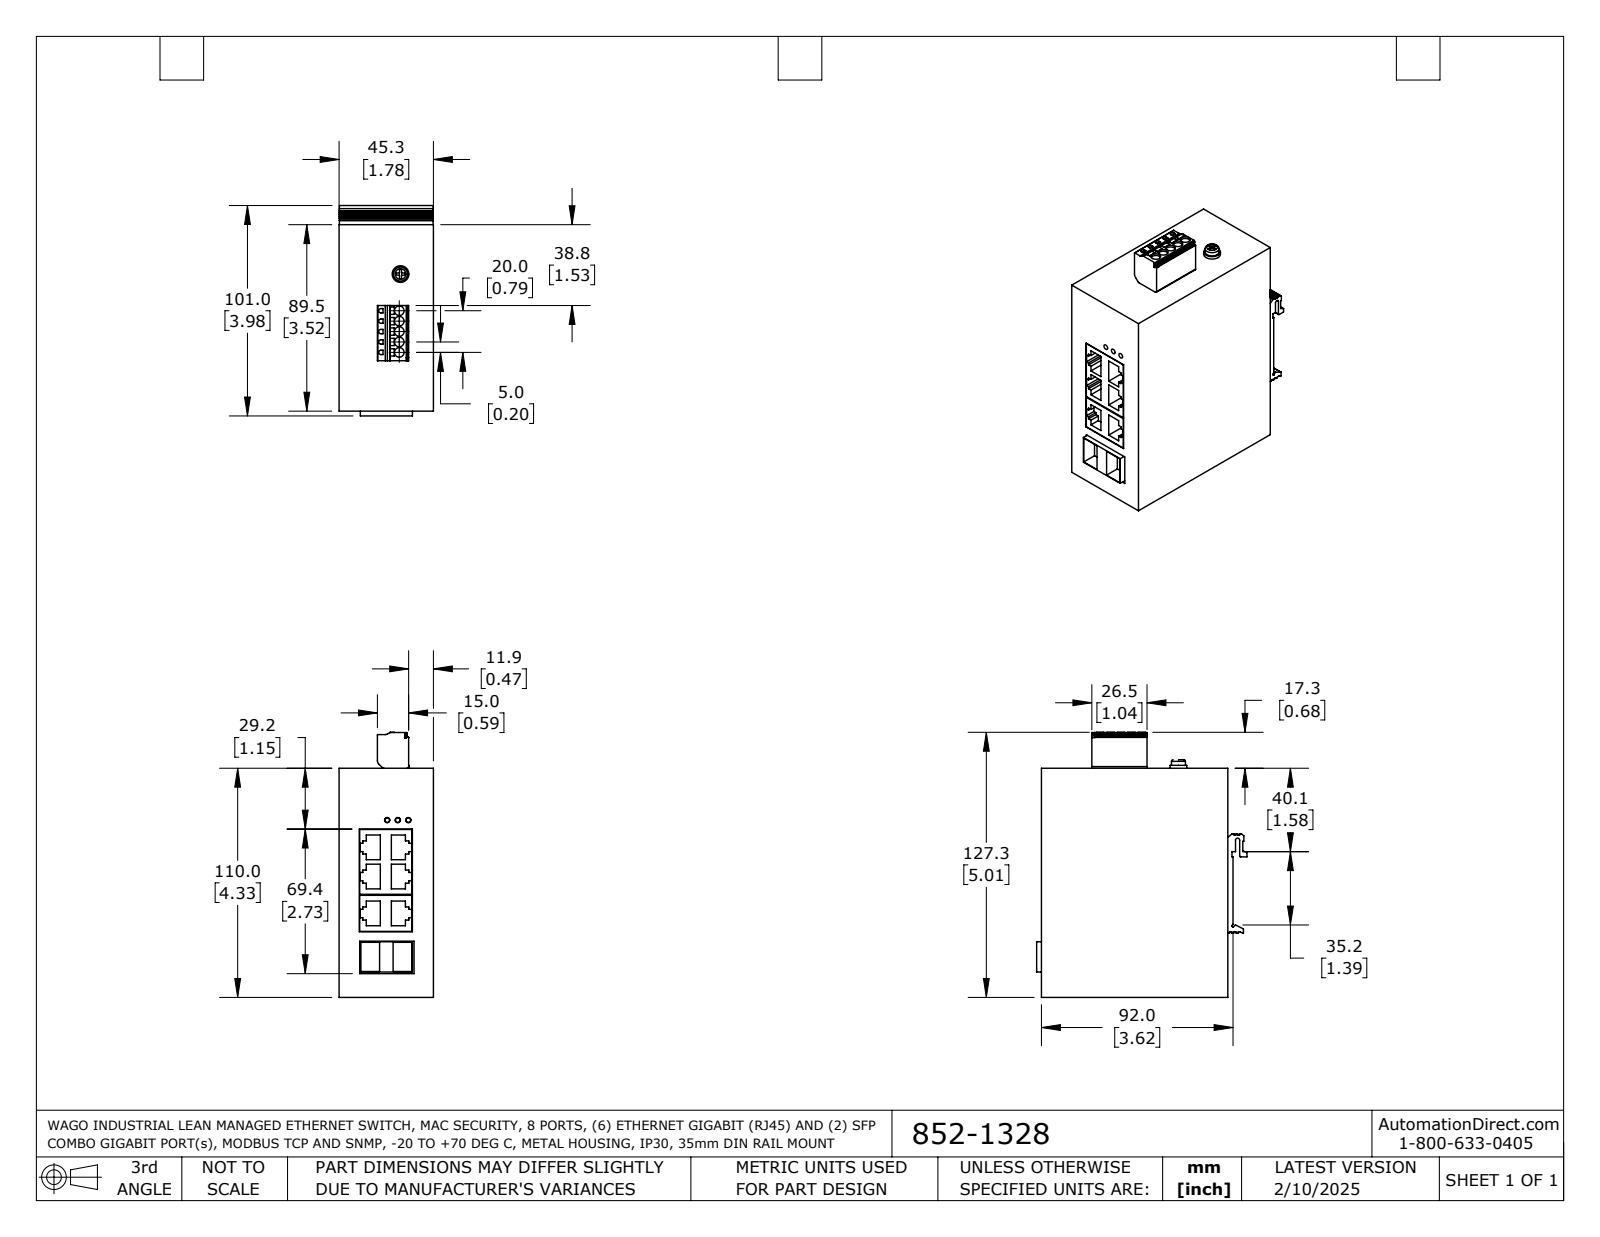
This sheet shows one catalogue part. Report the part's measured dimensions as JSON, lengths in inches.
{"part_name": "852-1328", "step_written_by": "SolidWorks 2021 (AUTOMOTIVE_DESIGN)", "units": "inches", "bodies": {"solids": 1, "faces": 348, "planar": 255, "cylindrical": 88, "other": 5}, "overall_size": [5.01, 3.976, 1.783], "volume_in3": 27.61, "surface_area_in2": 74.19, "round_holes": [[0.181, 5], [0.098, 3]], "round_bosses_or_shafts": [[0.315, 1], [0.264, 1]], "partial_cylinders_radius": [[0.004, 46], [0.041, 5], [0.02, 4], [0.008, 3], [0.031, 1], [0.039, 1], [0.047, 1], [0.079, 1]], "face_to_face_distances": [1.783, 4.331, 3.524, 3.622, 0.098, 0.39, 0.988, 0.398, 0.079, 0.197], "hole_center_spacings": [0.197, 0.394, 0.2, 0.591, 0.4, 0.787]}
